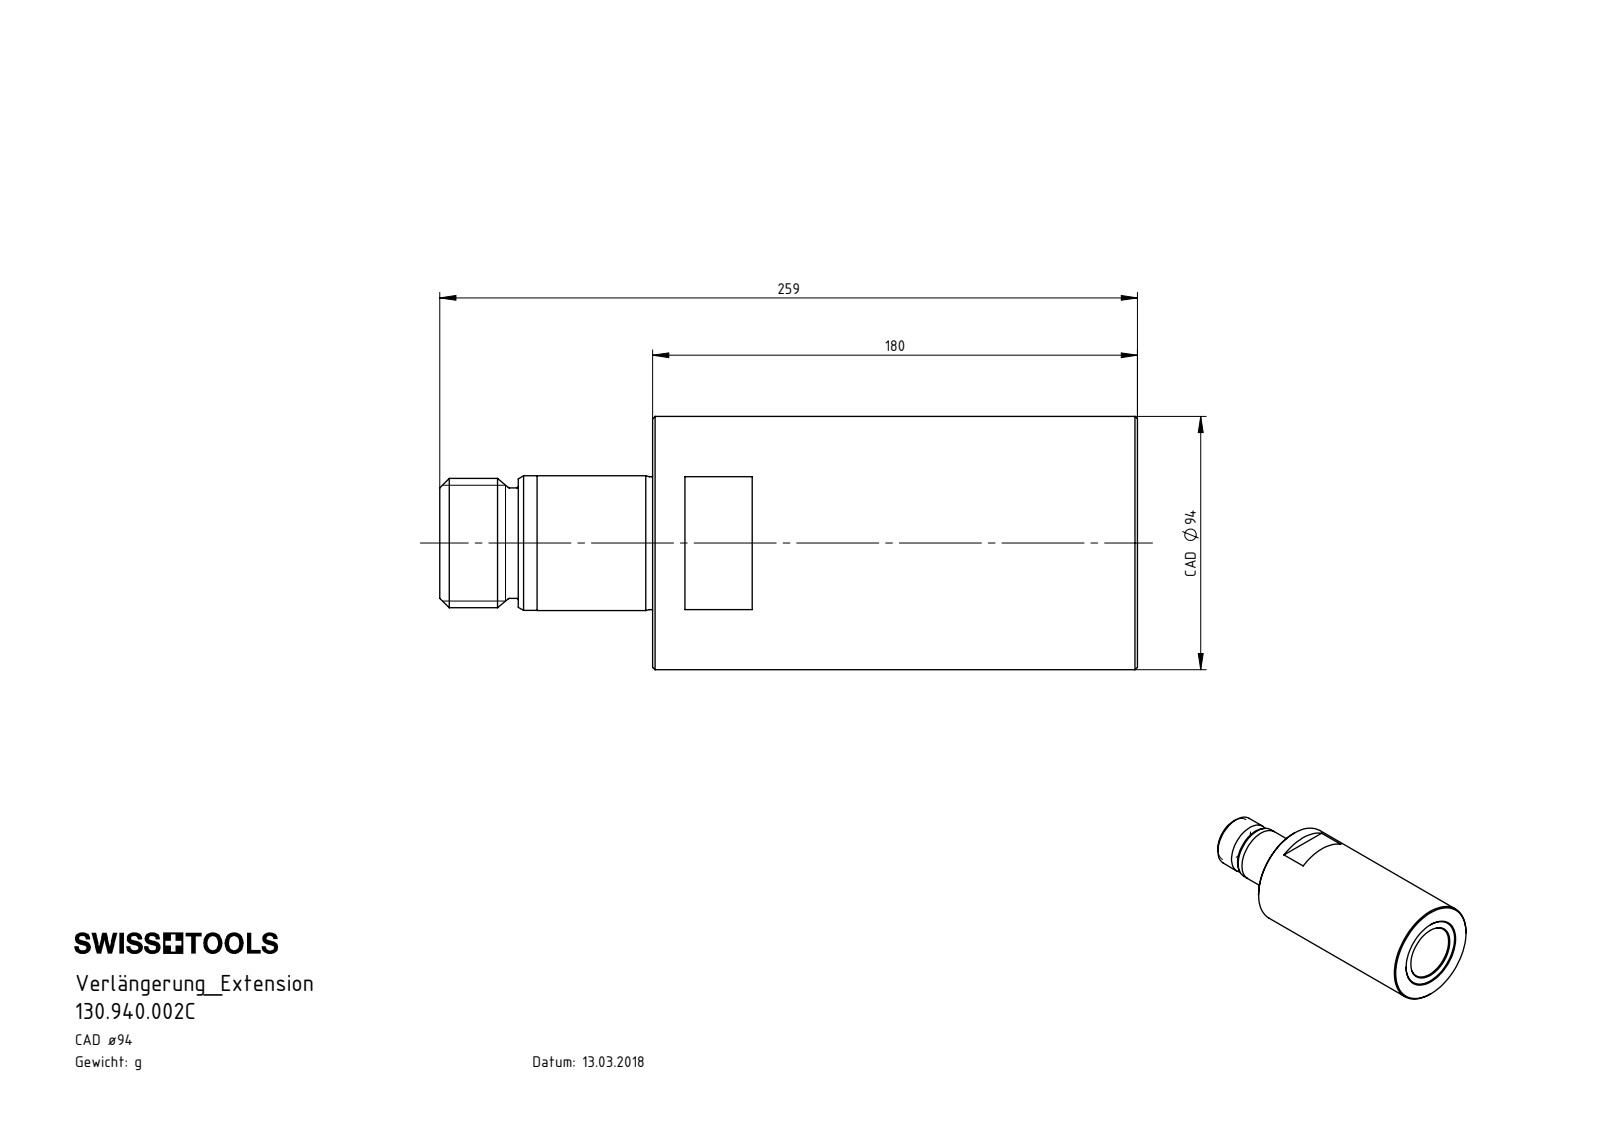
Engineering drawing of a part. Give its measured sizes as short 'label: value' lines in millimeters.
name: 130.940.002C
written by: SolidWorks 2017 (CONFIG_CONTROL_DESIGN)
unit: mm
bodies: 1 solid, 71 faces (13 planar, 20 cylindrical, 38 other)
size: 259 × 94 × 94
volume: 1 187 000 mm³; area: 99 029 mm²
holes: 1× ⌀8.5, 1× ⌀43, 1× ⌀50, 1× ⌀50.6
bosses: 1× ⌀94, 1× ⌀49.95, 1× ⌀49.3, 1× ⌀48, 1× ⌀41
face distances: 180, 79, 259, 80, 258.3, 179.3, 0.7, 91, 116, 12
